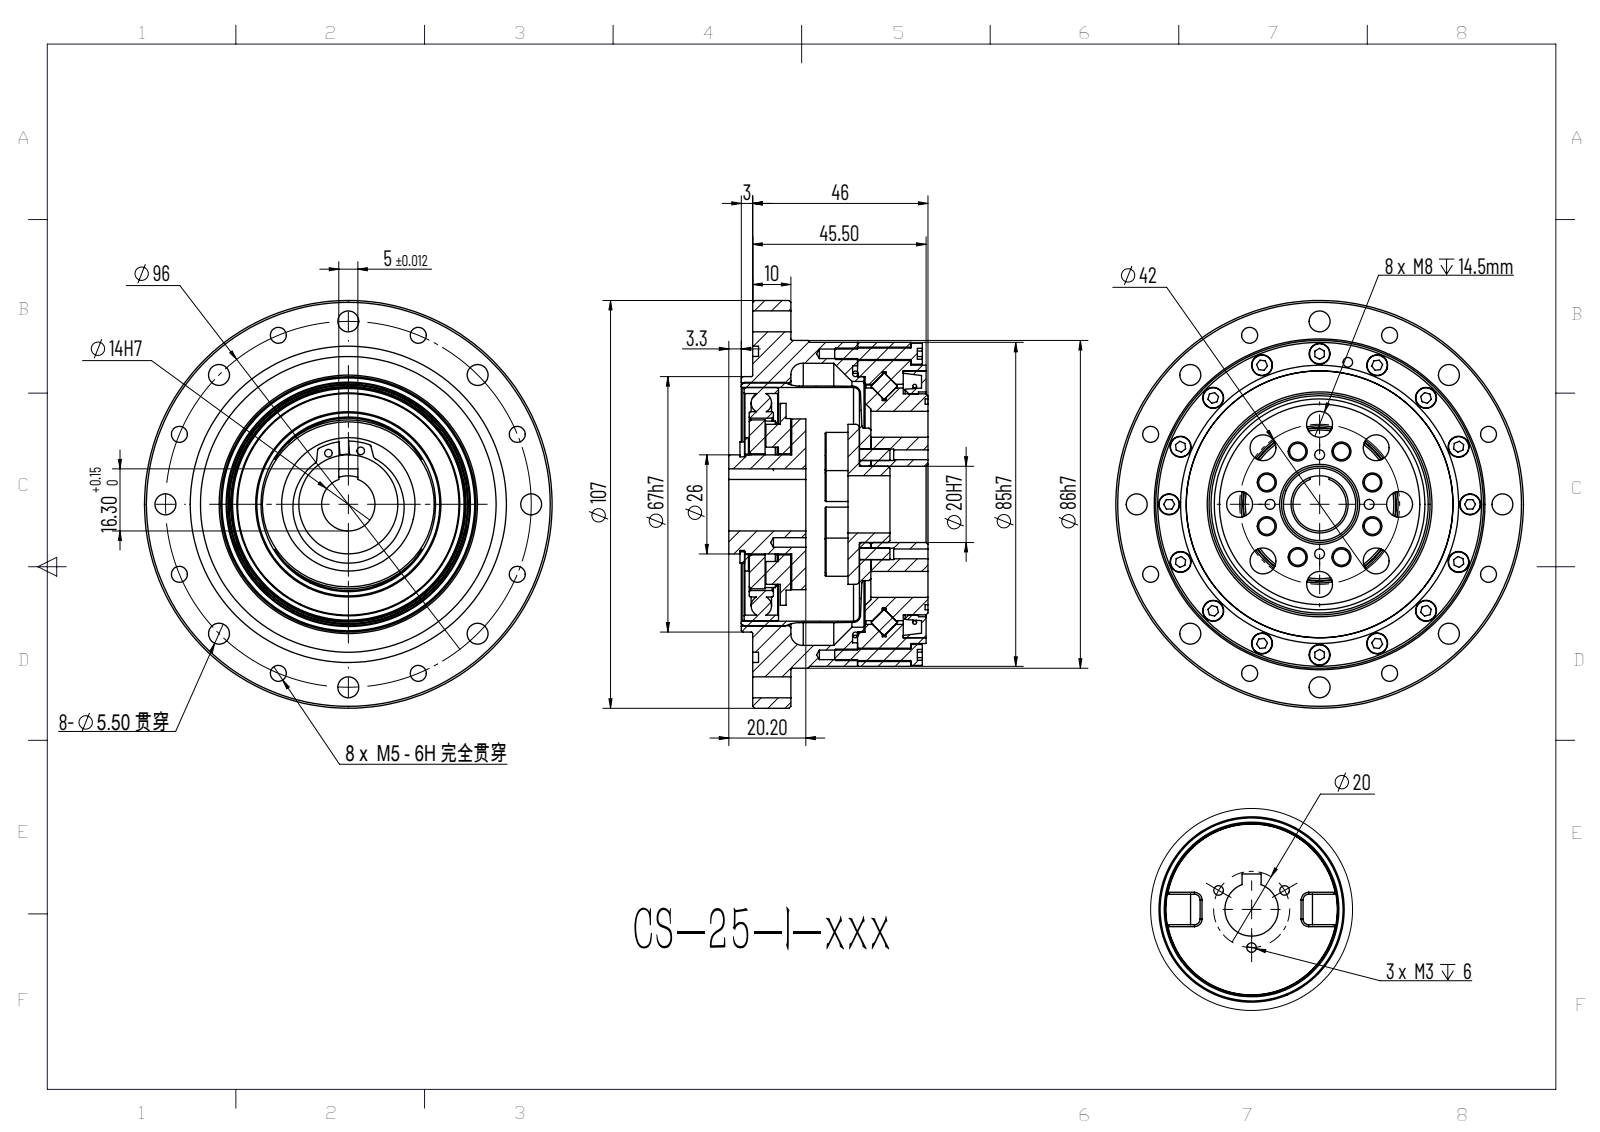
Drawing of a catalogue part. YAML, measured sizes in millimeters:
part_name: "CS-25-I; hexagon socket head cap screws gb_GB_FASTENER_SCREWS_HSHCS M3X12-C; 25-160??; ??????? (+8 more)"
step_written_by: "ONSHAPE BY PTC INC, 1.201 (AP242_MANAGED_MODEL_BASED_3D_ENGINEERING_MIM_LF)"
units: millimeters
bodies: {solids: 87, faces: 1094, planar: 559, cylindrical: 266, other: 269}
overall_size: [107, 107, 52.3]
volume: 201934
surface_area: 128595
round_holes:
  - {diameter: 2.5, count: 20}
  - {diameter: 3.5, count: 16}
  - {diameter: 3, count: 8}
  - {diameter: 4.2, count: 8}
  - {diameter: 5, count: 8}
  - {diameter: 5.5, count: 8}
  - {diameter: 6.6, count: 8}
  - {diameter: 6.8, count: 8}
  - {diameter: 2.6, count: 4}
  - {diameter: 2, count: 2}
  - {diameter: 3.2, count: 1}
  - {diameter: 5.8, count: 1}
round_bosses_or_shafts:
  - {diameter: 4, count: 48}
  - {diameter: 5.5, count: 16}
  - {diameter: 3, count: 16}
  - {diameter: 10, count: 8}
  - {diameter: 6, count: 8}
  - {diameter: 107, count: 1}
  - {diameter: 86, count: 1}
  - {diameter: 85, count: 1}
partial_cylinders:
  - {radius: 0.5, count: 2}
  - {radius: 1, count: 2}
  - {radius: 16.6, count: 1}
face_to_face_distances: [18, 1.5, 17.5, 10, 0.5, 3, 27.5, 28, 29.5, 21]
hole_center_spacings: [55.5, 50.29, 94.16, 34.62, 38.87, 48, 79.82, 88.69]
